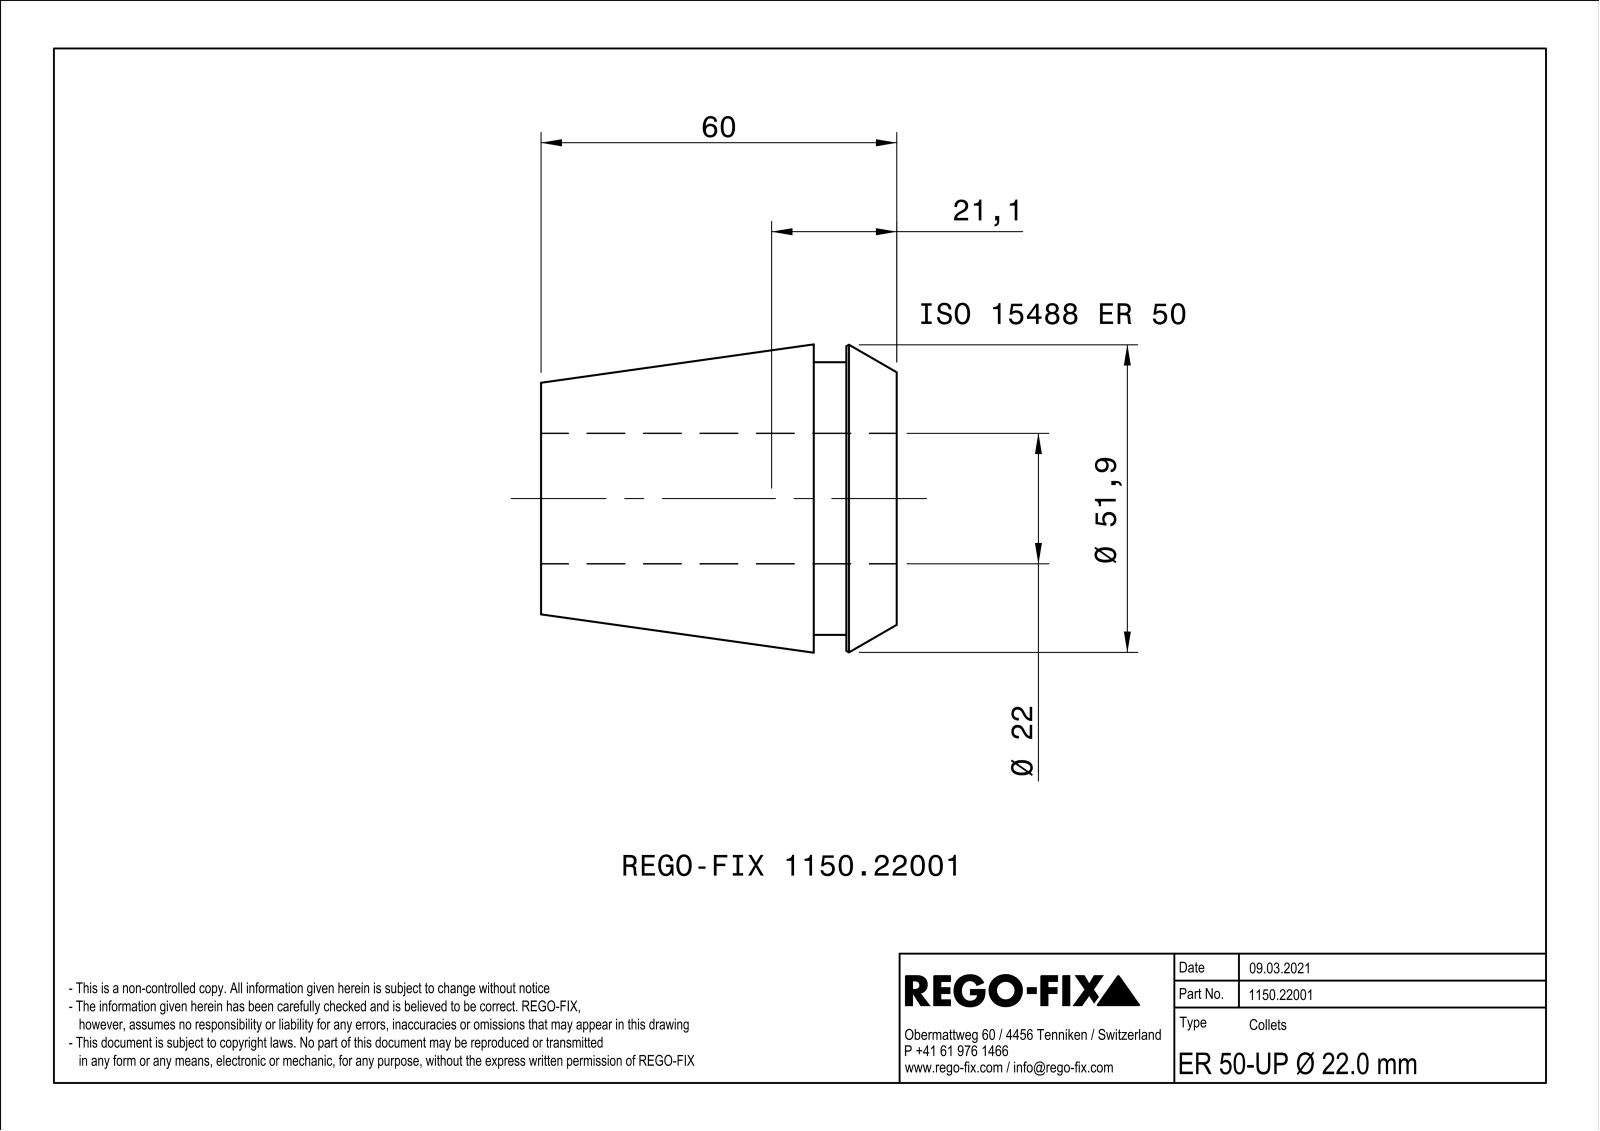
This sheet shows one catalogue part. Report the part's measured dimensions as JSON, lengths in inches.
{"part_name": "NOCUT", "step_written_by": "SIEMENS PLM Software Solid Edge ST10 (AUTOMOTIVE_DESIGN)", "units": "inches", "bodies": {"solids": 1, "faces": 177, "planar": 88, "cylindrical": 9, "other": 80}, "overall_size": [2.362, 2.047, 2.047], "volume_in3": 4.063, "surface_area_in2": 53.39, "round_holes": [[0.866, 1]], "round_bosses_or_shafts": [[1.811, 1]], "face_to_face_distances": [0.039, 2.362, 0.551, 1.811, 0.335, 0.217, 2.028, 0.354, 0.02, 0.197]}
